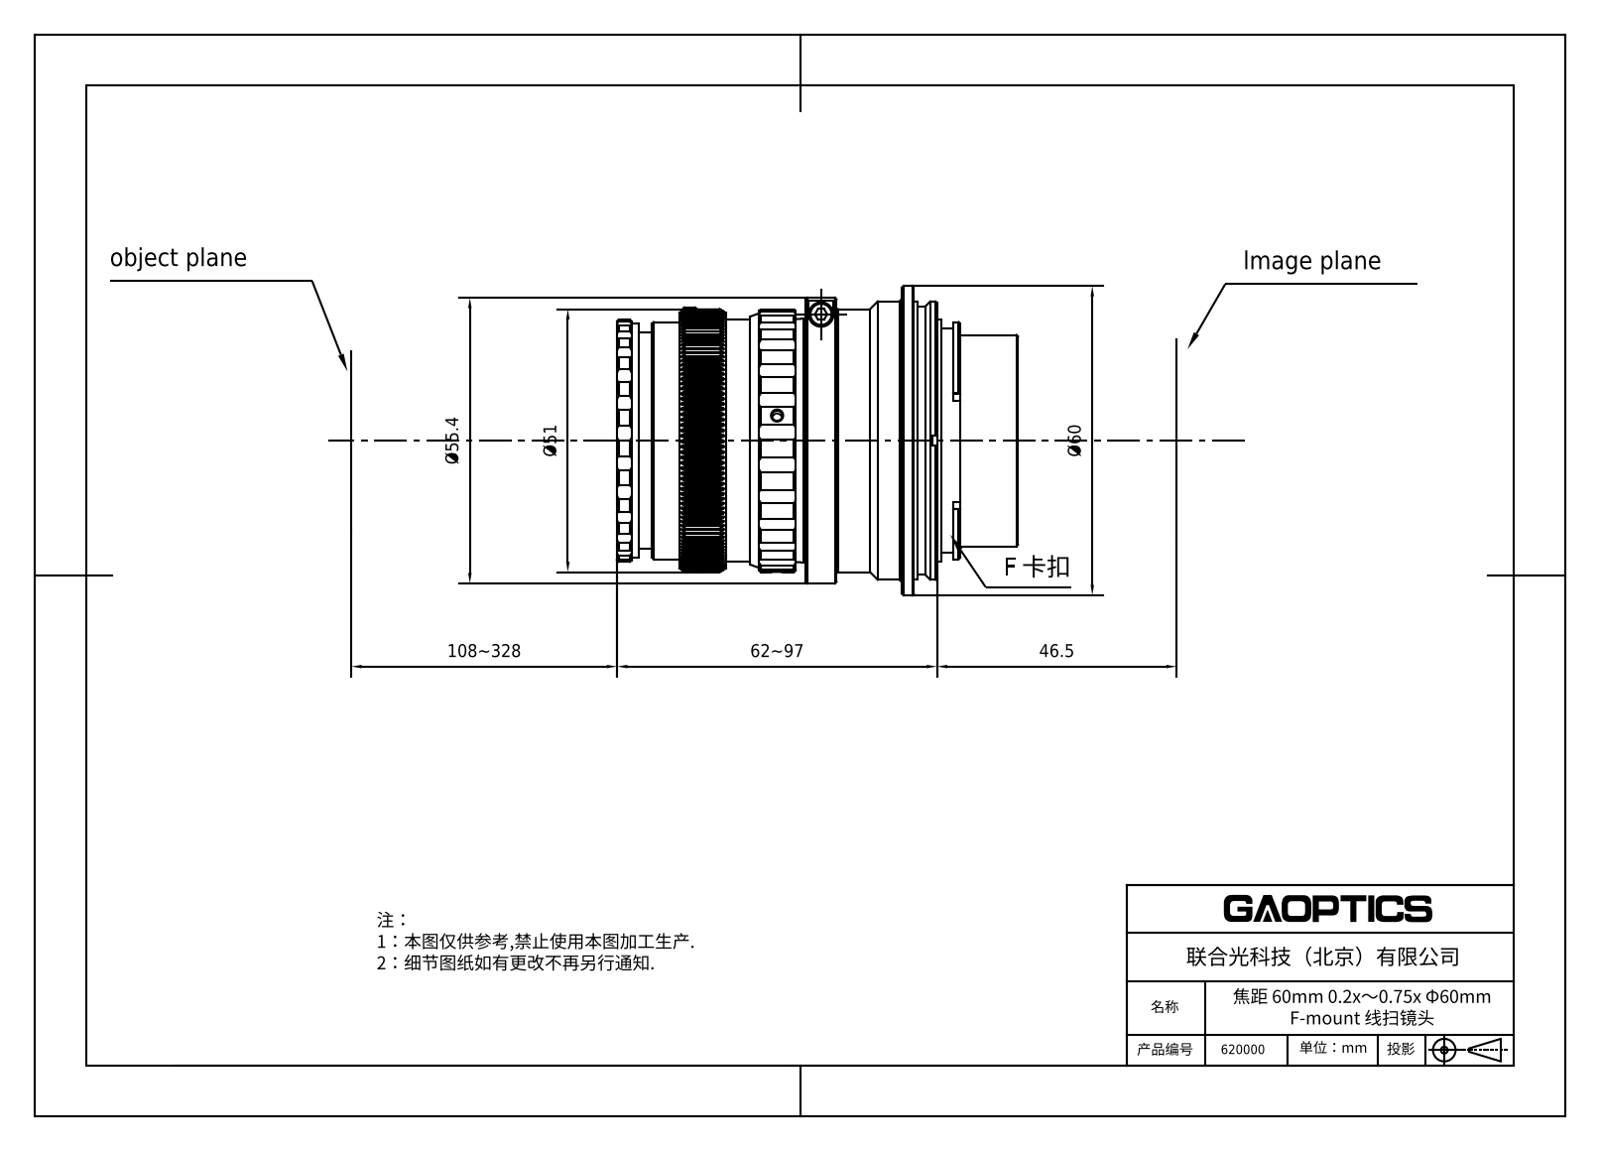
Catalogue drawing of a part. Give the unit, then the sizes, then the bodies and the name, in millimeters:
Units: millimetres
Overall size (bounding box): 77.81 × 60 × 59.99
Round holes (diameter × count): ⌀2 ×5, ⌀1.4 ×1, ⌀1.5 ×1, ⌀2.6 ×1, ⌀11 ×1, ⌀16.17 ×1, ⌀19 ×1, ⌀21.2 ×1, ⌀23.6 ×1, ⌀24 ×1, ⌀25 ×1, ⌀25.6 ×1
Round bosses / shafts (diameter × count): ⌀2.5 ×2, ⌀60 ×1, ⌀55.4 ×1, ⌀54 ×1, ⌀52 ×1, ⌀51 ×1, ⌀47.2 ×1, ⌀47 ×1
Partial cylindrical surfaces — rounded edges, fillets, slot ends (radius × count): R0.2 ×150, R2.5 ×50, R1 ×7, R5 ×4, R0.75 ×1, R1.75 ×1, R2.4 ×1, R4 ×1
Main face-to-face distances: 4.5, 4.1, 6, 28.28, 12.49, 18.49, 6.82, 19.31, 25.31, 10.83
Hole centre spacings: 4, 7.75, 11.75, 16.95, 20.95, 28.7
Volume: 87 771 mm³ · Surface area: 64 562 mm²
Bodies: 17 solids, 1557 faces (535 planar, 732 cylindrical, 290 other)
Part name (STEP PRODUCT): 620000
STEP written by: SolidWorks 2016 (CONFIG_CONTROL_DESIGN)
